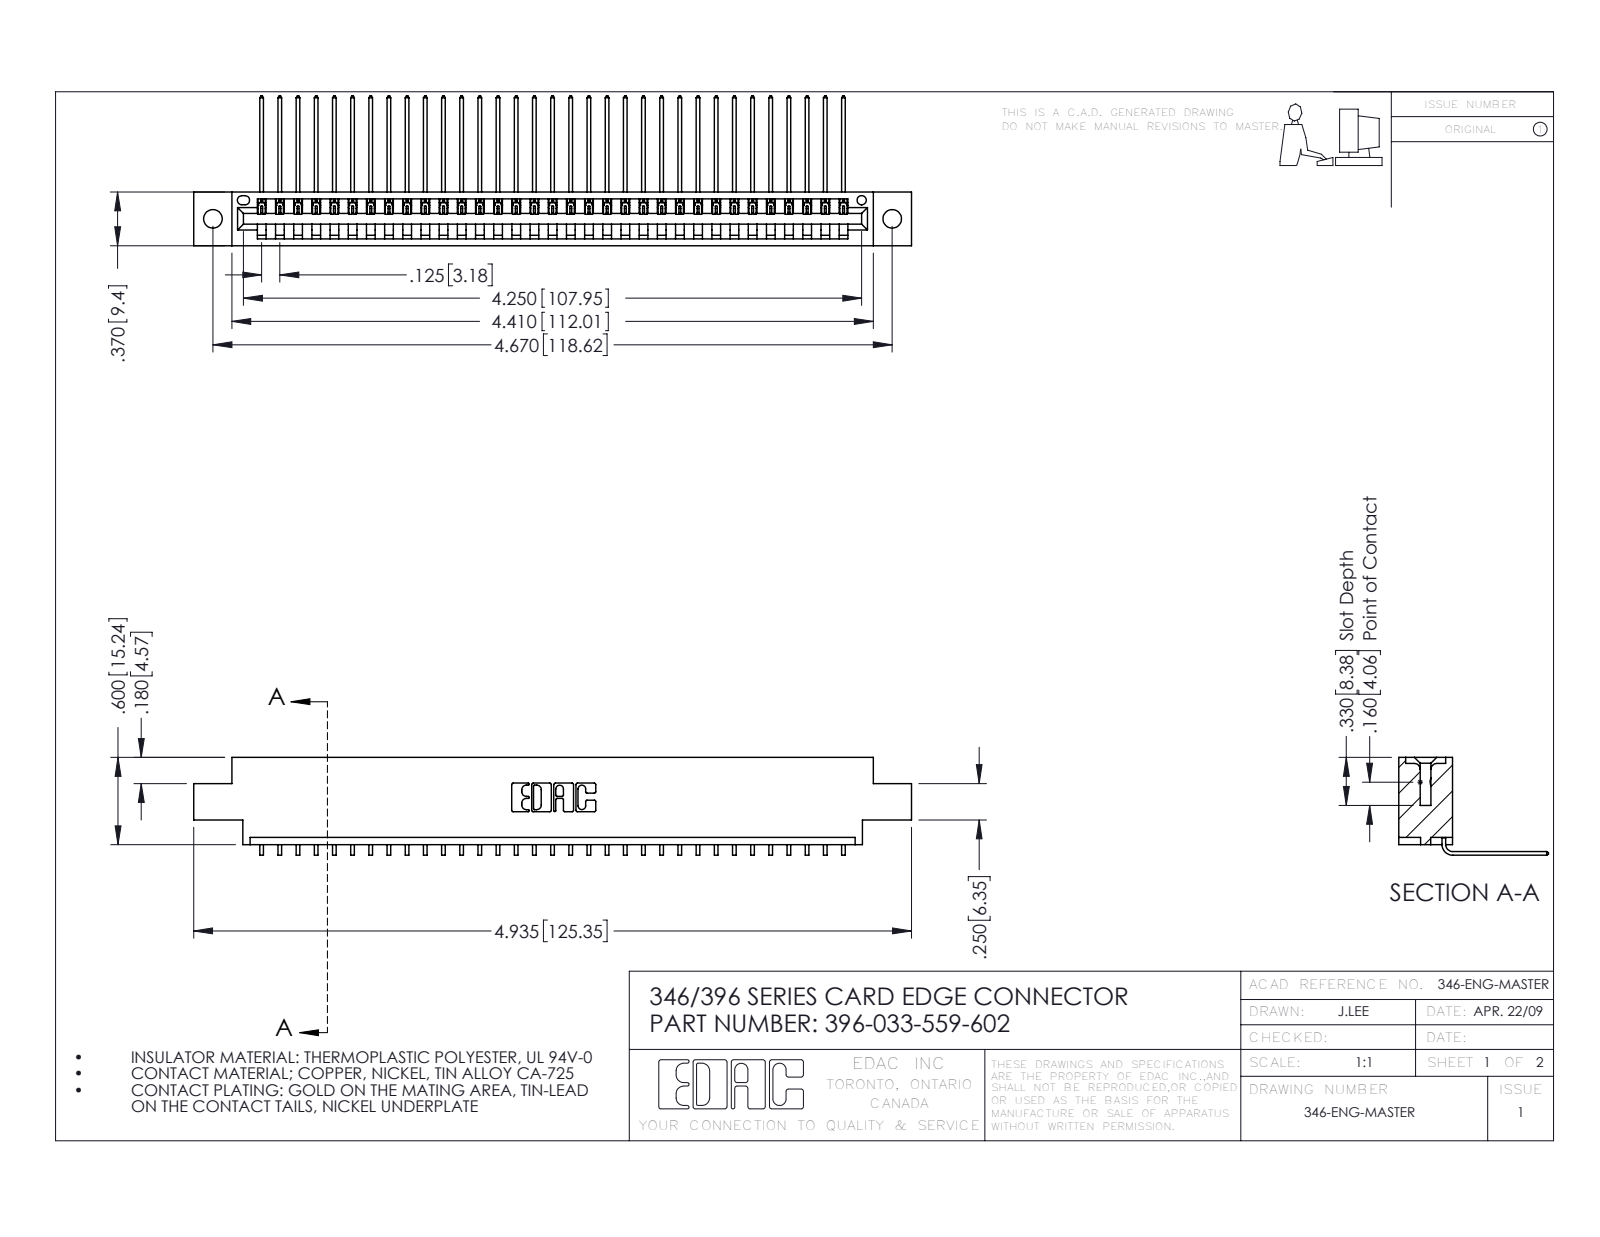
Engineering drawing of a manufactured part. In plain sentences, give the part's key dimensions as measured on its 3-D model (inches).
The part is named "346 Part_0.170 Offset - 0.128 Dia; 345-292-001_558 559 Tail - 1; 396-033-559-602". Its 3-D file was written by "SolidWorks 2016 (CONFIG_CONTROL_DESIGN)". It is 34 solids with 2106 faces: 1466 planar, 640 cylindrical and 0 other. Overall it measures 4.935 by 1.03 by 0.673 inches. Its volume is 0.723 cubic inches and its surface area 23.66 square inches. Round holes: 2 of diameter 0.128, 1 of diameter 0.064. Partial cylindrical surfaces (rounded edges, fillets, slot ends): 66 of radius 0.006, 22 of radius 0.01, 6 of radius 0.007, 6 of radius 0.031, 3 of radius 0.026, 2 of radius 0.031, 2 of radius 0.04, 1 of radius 0.014. The main face-to-face distances are 0.048, 0.322, 0.37, 0.025, 0.25, 0.072, 0.298, 0.148, 0.222, 0.1. The hole center spacings are 0.246, 4.462, 4.67.
